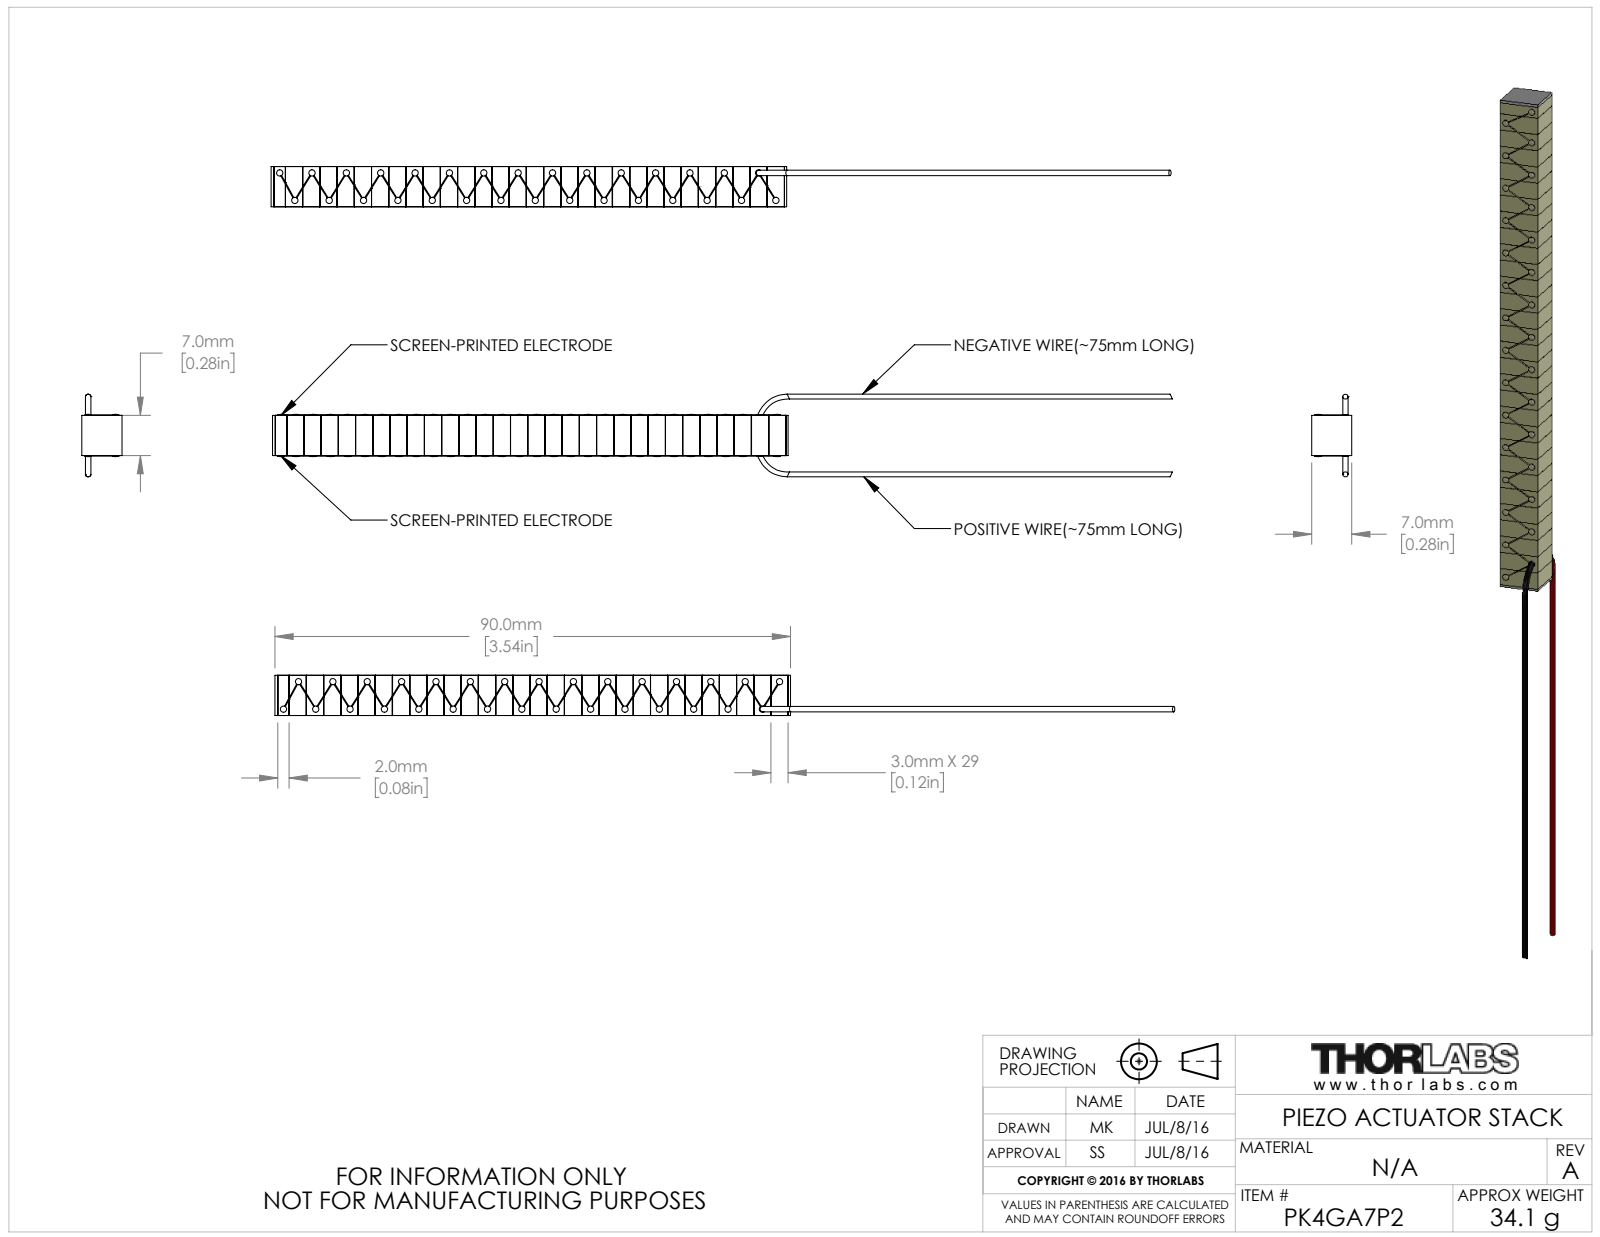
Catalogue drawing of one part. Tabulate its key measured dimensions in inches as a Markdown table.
| quantity | value |
| --- | --- |
| part name | CTN009153 |
| STEP written by | SolidWorks 2016 (AUTOMOTIVE_DESIGN) |
| units | inches |
| bodies | 4 solids, 914 faces (550 planar, 120 cylindrical, 244 other) |
| overall size | 6.187 × 0.568 × 0.276 |
| volume | 0.541 in³ |
| surface area | 18.04 in² |
| round bosses / shafts (diameter × count) | 0.043 × 30 |
| main face-to-face distances | 0.276, 0.237, 0.473, 0.71, 0.946, 1.183, 1.42, 0.355, 1.065, 0.118 |
